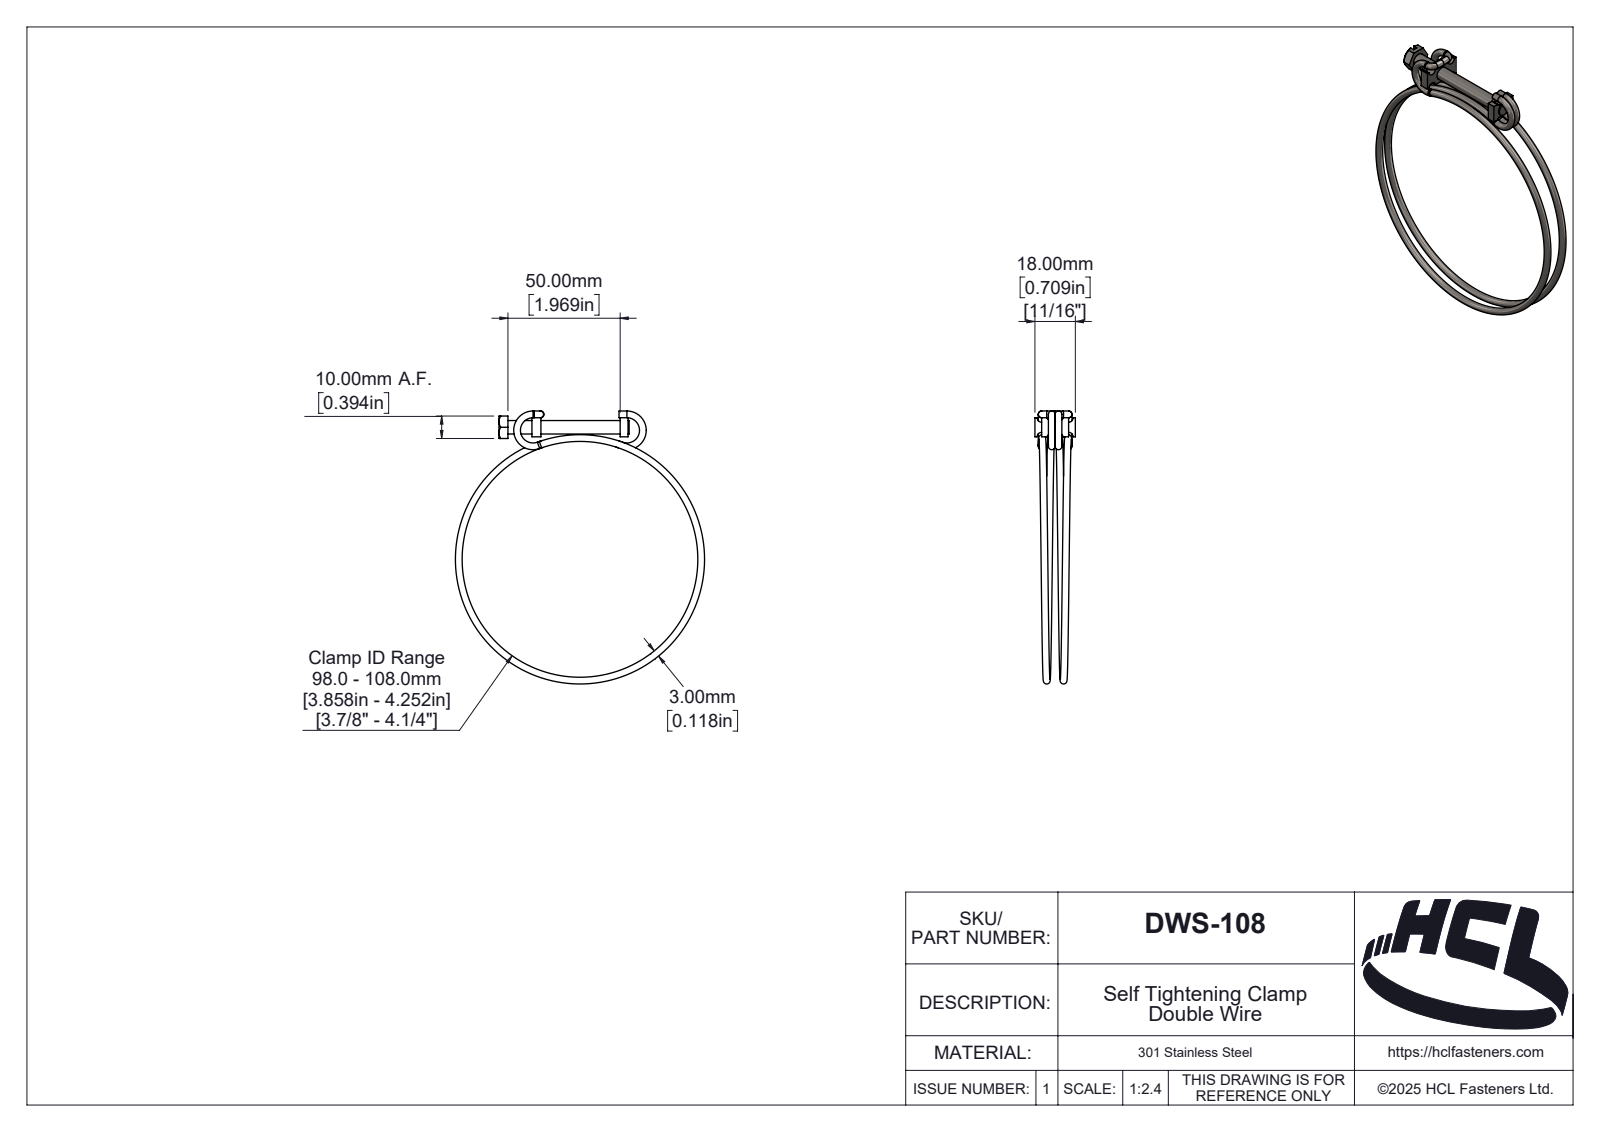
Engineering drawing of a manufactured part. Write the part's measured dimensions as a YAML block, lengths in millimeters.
part_name: "DWS-108"
step_written_by: "SolidWorks 2025 (AUTOMOTIVE_DESIGN)"
units: millimeters
bodies: {solids: 6, faces: 213, planar: 55, cylindrical: 74, other: 84}
overall_size: [121.55, 111, 18]
volume: 8635
surface_area: 10515
round_holes:
  - {diameter: 6, count: 1}
round_bosses_or_shafts:
  - {diameter: 3, count: 4}
partial_cylinders:
  - {radius: 0.2, count: 12}
  - {radius: 1, count: 4}
  - {radius: 2, count: 4}
  - {radius: 0.4, count: 1}
  - {radius: 0.51, count: 1}
  - {radius: 0.53, count: 1}
  - {radius: 0.64, count: 1}
  - {radius: 0.91, count: 1}
face_to_face_distances: [4, 14.7, 10, 39.3, 3, 54, 38.8, 53.5, 1, 42.8]
